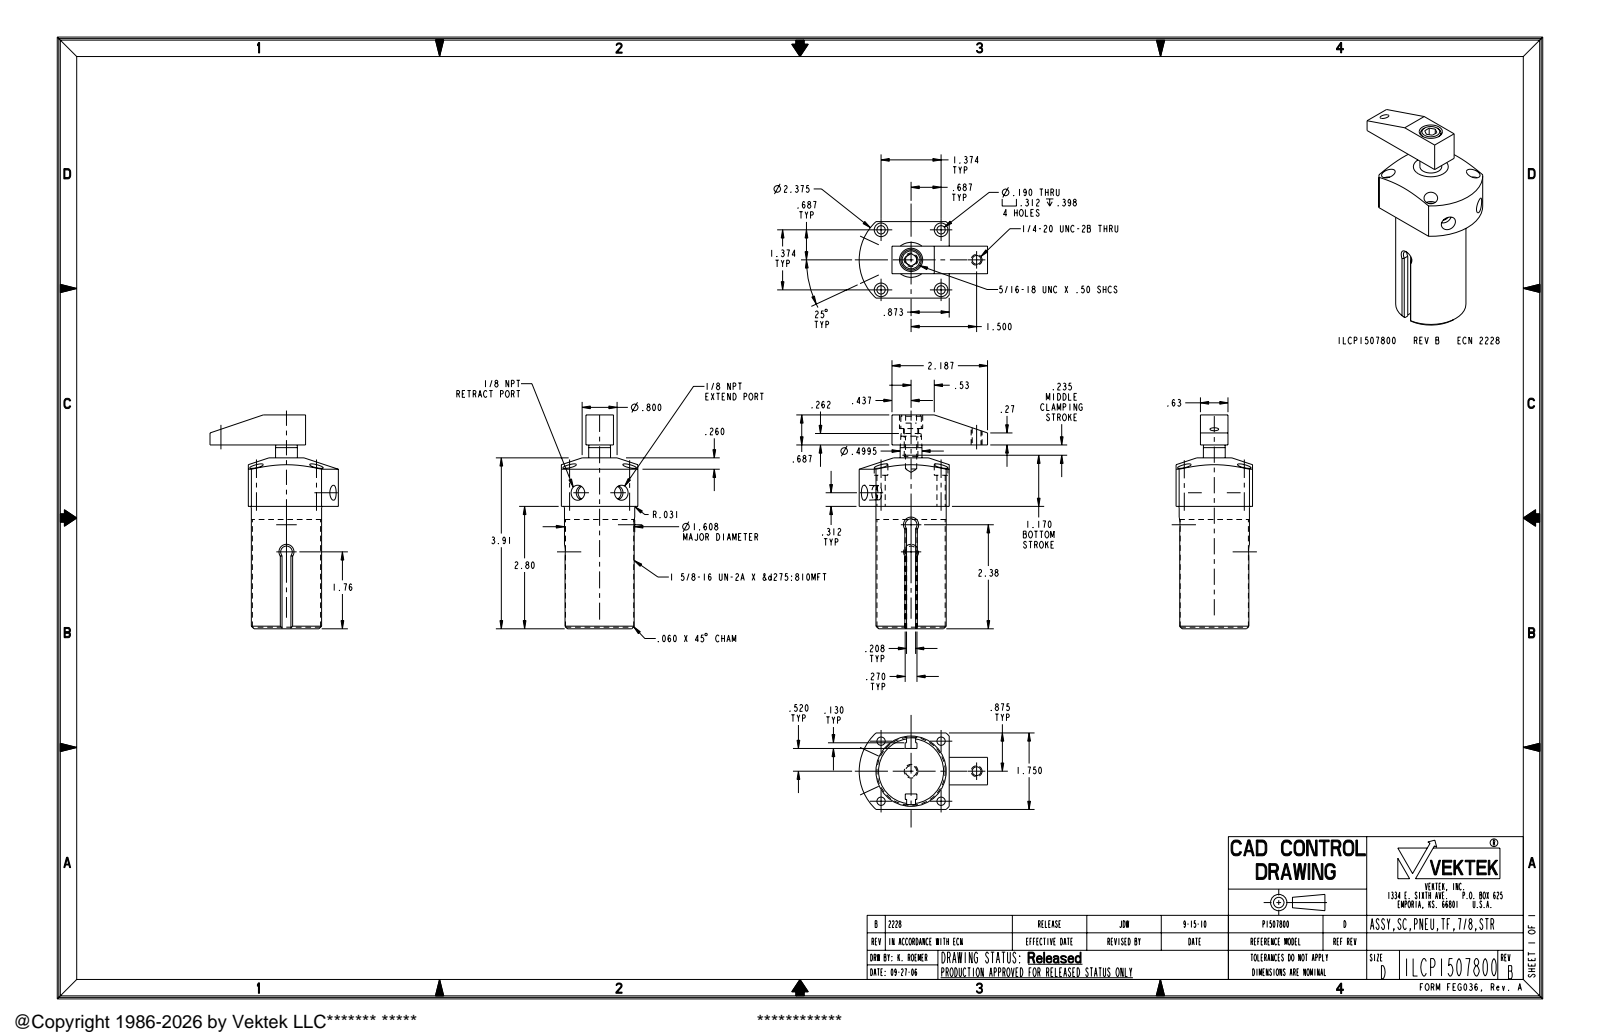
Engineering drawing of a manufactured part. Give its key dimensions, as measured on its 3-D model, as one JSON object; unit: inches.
{"part_name": "ILCP1507800; ILC91500903; ILCP1507800_ASM", "step_written_by": "PRO/ENGINEER BY PARAMETRIC TECHNOLOGY CORPORATION, 2007460 (AUTOMOTIVE_DESIGN_CC2)", "units": "inches", "bodies": {"solids": 2, "faces": 123, "planar": 52, "cylindrical": 47, "other": 24}, "overall_size": [4.892, 2.938, 1.75], "volume_in3": 9.334, "surface_area_in2": 55.05, "round_holes": [[0.19, 4], [0.312, 4], [0.328, 2], [0.201, 1], [0.257, 1], [0.344, 1], [0.531, 1]], "round_bosses_or_shafts": [[1.608, 1], [1.562, 1], [0.5, 1], [0.469, 1], [0.312, 1], [0.25, 1]], "partial_cylinders_radius": [[0.132, 1], [0.135, 1], [1.187, 1]], "face_to_face_distances": [1.75, 0.562, 1.192, 0.558, 0.63, 1.188, 0.355, 1.395, 4.205, 1.405], "hole_center_spacings": [0.972, 1.374, 1.065, 1.943, 2.293, 1.5]}
